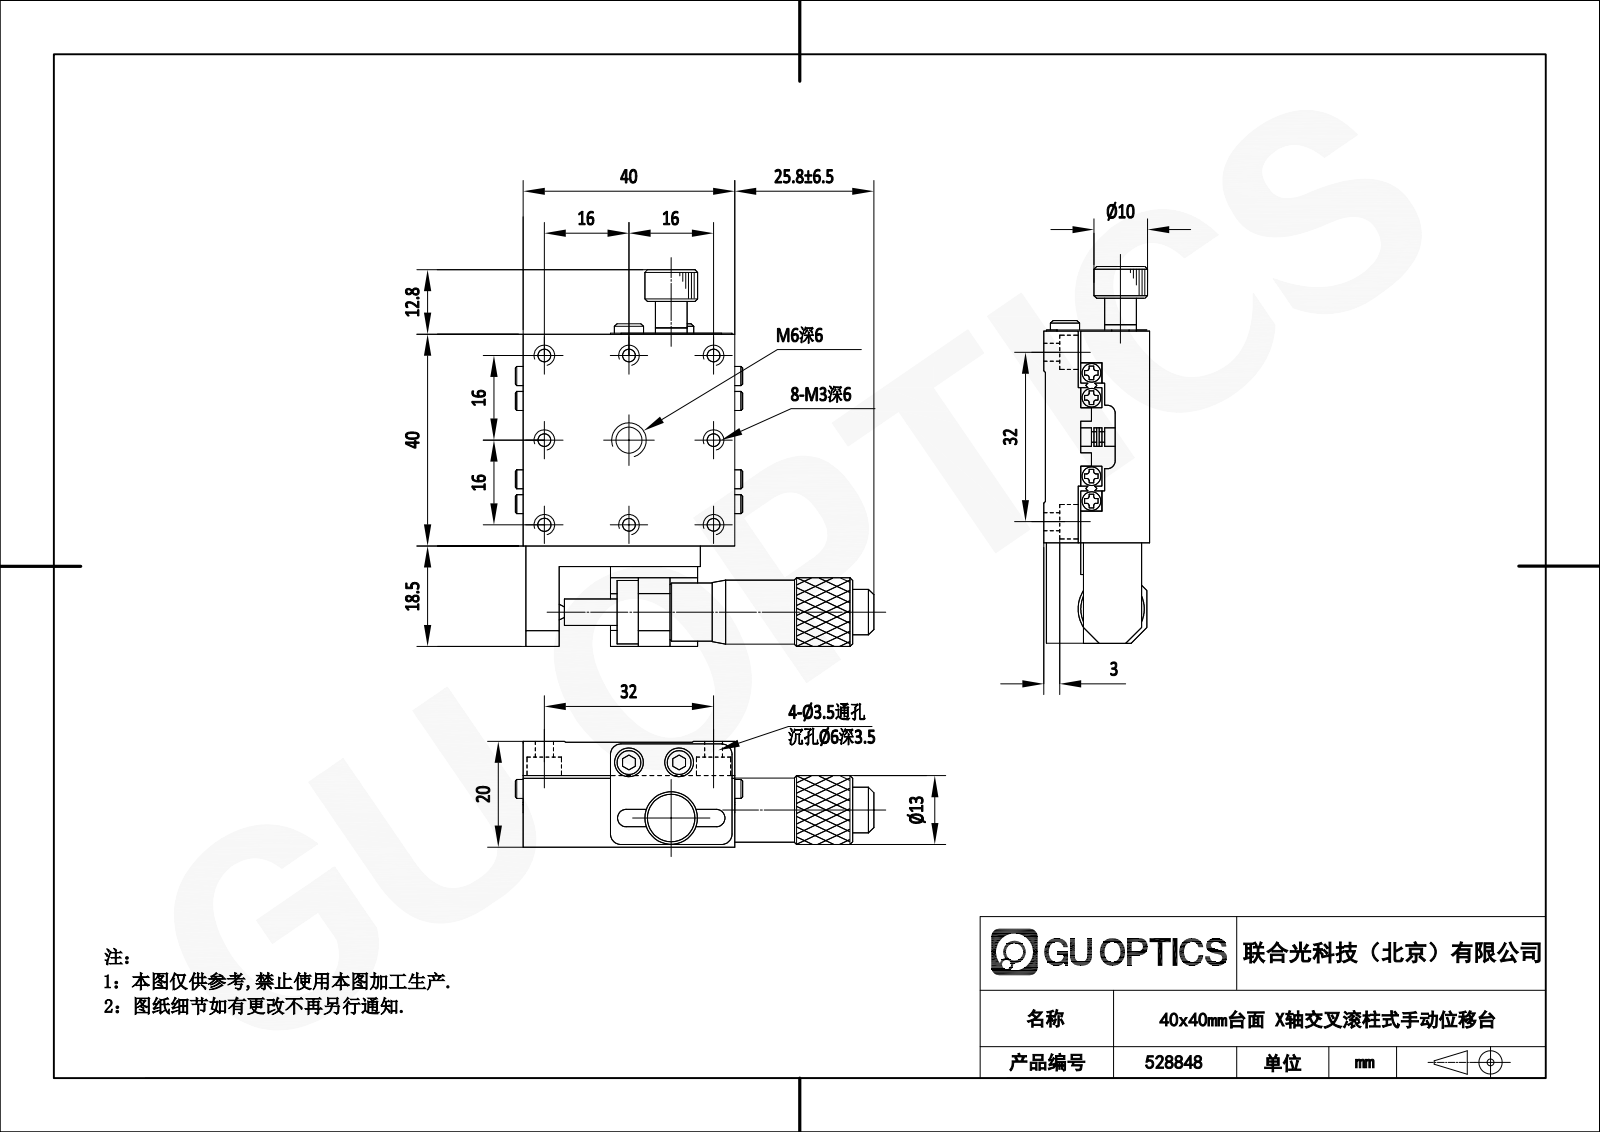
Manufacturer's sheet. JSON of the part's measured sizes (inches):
{"part_name": "528848", "step_written_by": "SolidWorks 2020 (CONFIG_CONTROL_DESIGN)", "units": "inches", "bodies": {"solids": 3, "faces": 2526, "planar": 302, "cylindrical": 552, "other": 1672}, "overall_size": [2.827, 2.669, 0.787], "volume_in3": 2.205, "surface_area_in2": 33.52, "round_holes": [[0.097, 12], [0.098, 10], [0.173, 8], [0.236, 8], [0.097, 7], [0.062, 6], [0.126, 5], [0.062, 4], [0.11, 4], [0.138, 4], [0.079, 2], [0.079, 2]], "round_bosses_or_shafts": [[0.157, 4], [0.236, 2], [0.134, 2], [0.079, 2], [0.512, 1], [0.492, 1], [0.413, 1], [0.335, 1]], "partial_cylinders_radius": [[0.079, 5], [0.068, 2], [0.197, 1], [0.295, 1]], "face_to_face_distances": [0.256, 0.276, 0.02, 0.531, 0.512, 0.787, 0.236, 1.575, 0.157, 0.039], "hole_center_spacings": [0.787, 0.63, 0.891, 1.409, 1.26, 0.348, 0.406, 1.055]}
